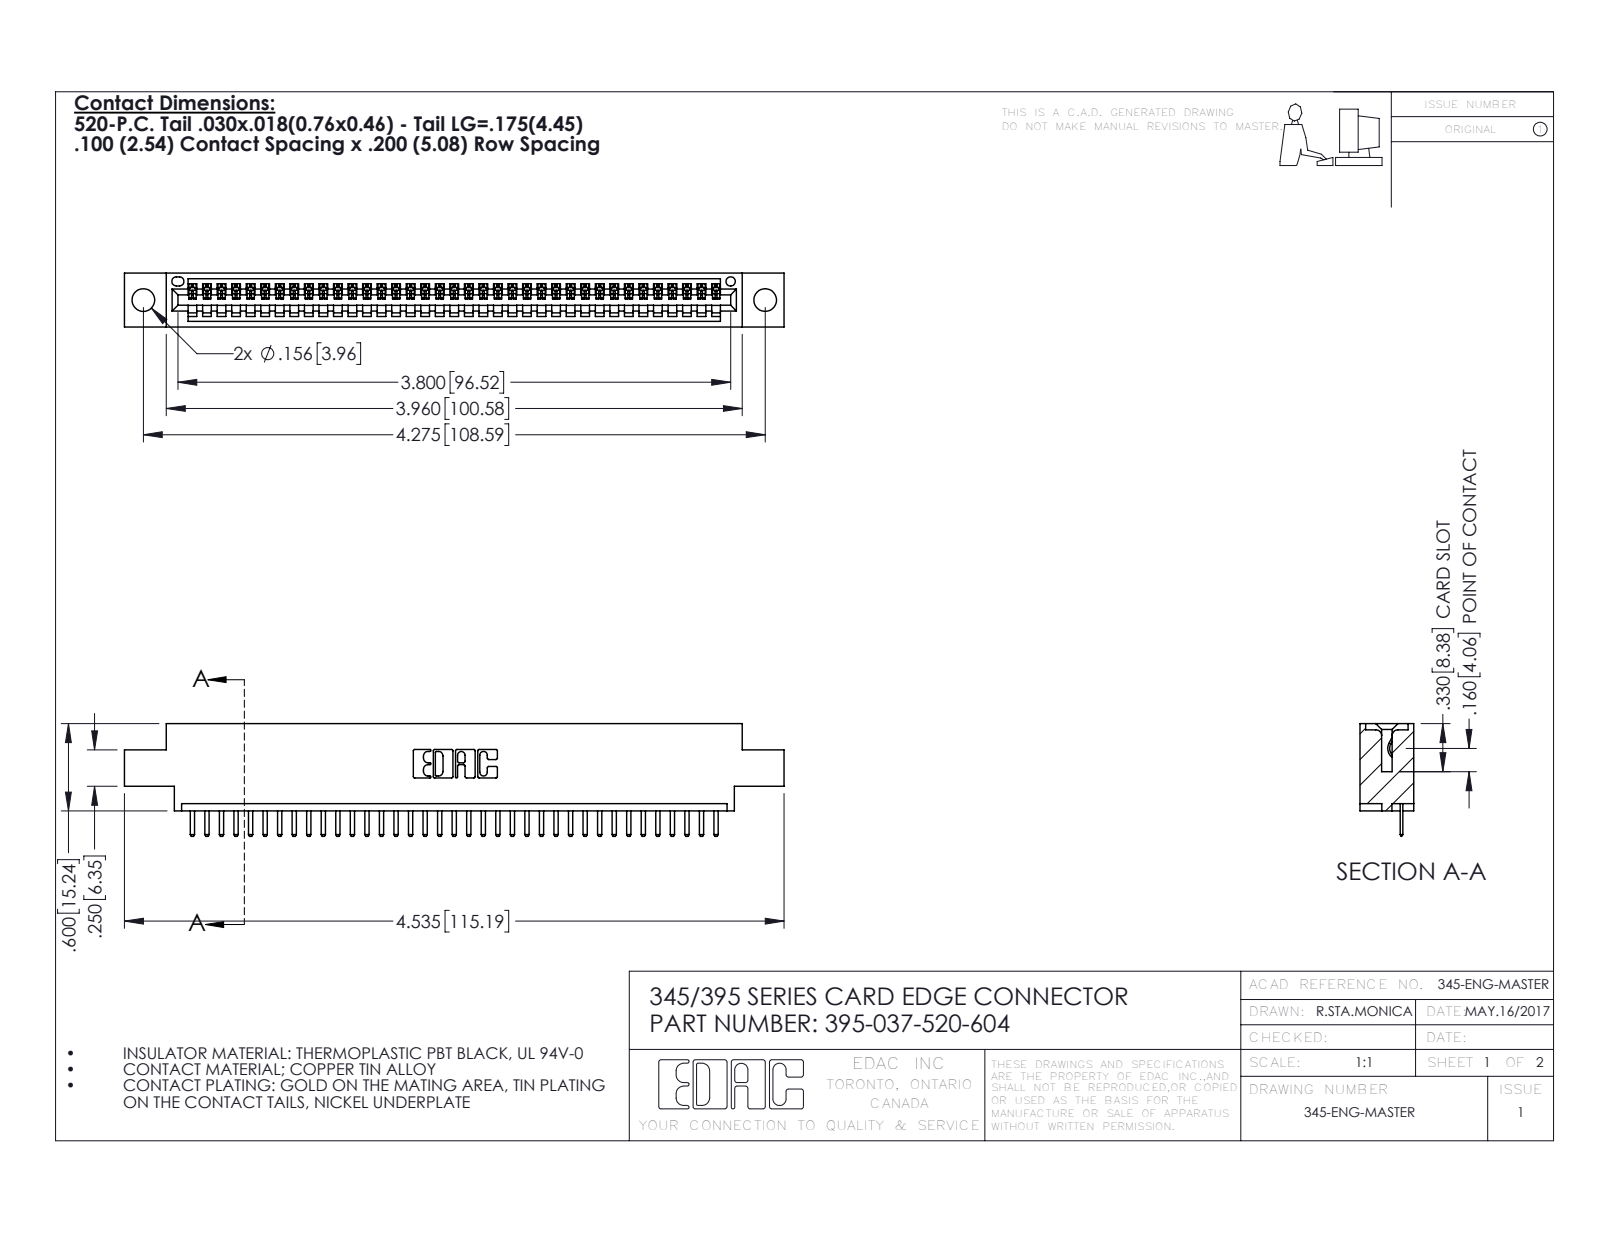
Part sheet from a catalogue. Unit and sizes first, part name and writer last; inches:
Units: inches
Overall size (bounding box): 4.535 × 0.775 × 0.37
Round holes (diameter × count): ⌀0.156 ×2, ⌀0.064 ×1
Partial cylindrical surfaces — rounded edges, fillets, slot ends (radius × count): R0.01 ×76, R0.006 ×74, R0.01 ×22, R0.007 ×6, R0.031 ×6, R0.026 ×3, R0.031 ×2, R0.04 ×2
Main face-to-face distances: 0.072, 0.298, 0.37, 0.2, 0.098, 0.272, 0.025, 0.225, 0.072, 0.175
Hole centre spacings: 0.27, 4.039, 4.275
Volume: 0.646 in³ · Surface area: 21.07 in²
Bodies: 38 solids, 2424 faces (1638 planar, 786 cylindrical, 0 other)
Part name (STEP PRODUCT): 345-292-001_345-293-120; 345 Part_0.170 Offset - 0.156 Dia-TH; 395-037-520-604
STEP written by: SolidWorks 2016 (CONFIG_CONTROL_DESIGN)
